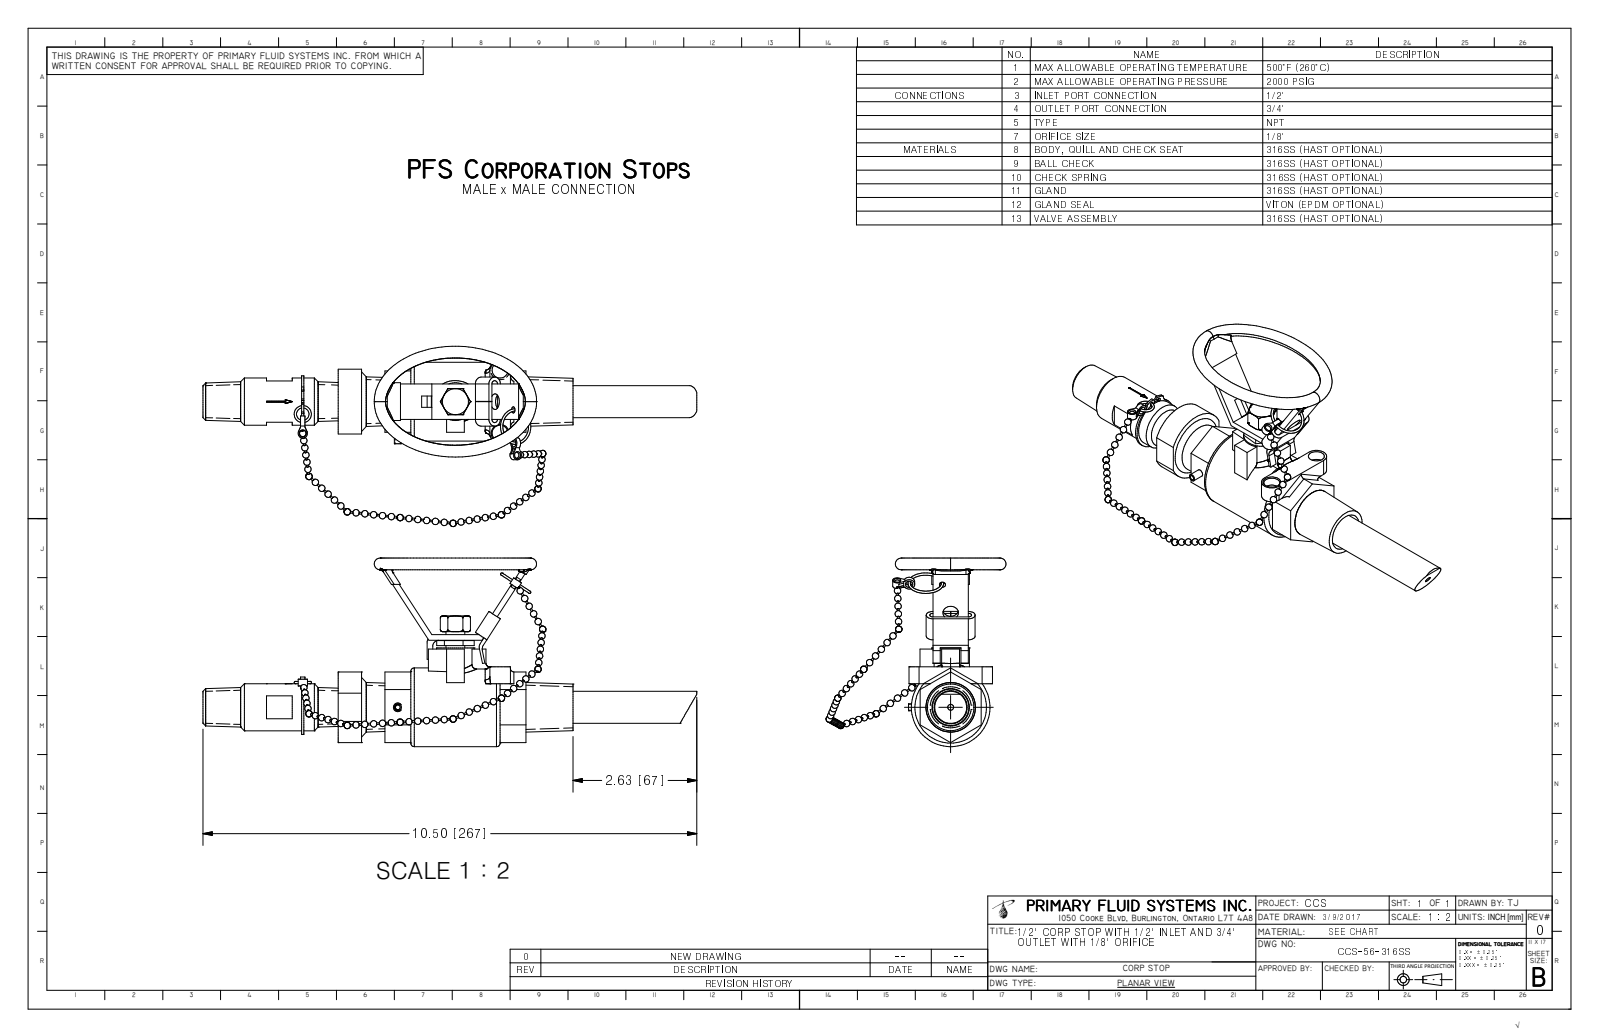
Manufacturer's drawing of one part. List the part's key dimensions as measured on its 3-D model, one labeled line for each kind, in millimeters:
Part name (STEP PRODUCT): CCS-56-316SS_R0
STEP written by: Autodesk Inventor 2009 (AUTOMOTIVE_DESIGN)
Units: millimetres
Bodies: 0 solids, 396 faces (182 planar, 42 cylindrical, 172 other)
Overall size (bounding box): 266.7 × 101.6 × 97.2
Round holes (diameter × count): ⌀2 ×1, ⌀3.2 ×1, ⌀6.4 ×1, ⌀11.9 ×1
Round bosses / shafts (diameter × count): ⌀42.4 ×1, ⌀27.8 ×1, ⌀25.4 ×1, ⌀20.3 ×1, ⌀17.2 ×1, ⌀10.2 ×1, ⌀3.8 ×1
Partial cylindrical surfaces — rounded edges, fillets, slot ends (radius × count): R1.9 ×4, R1.1 ×2, R1.3 ×2, R3.7 ×2, R3.8 ×2, R4 ×2, R3.2 ×1, R4.2 ×1
Main face-to-face distances: 33, 3, 14, 7, 26, 3, 25.2, 4.1, 62.2, 1
Hole centre spacings: 13.6
